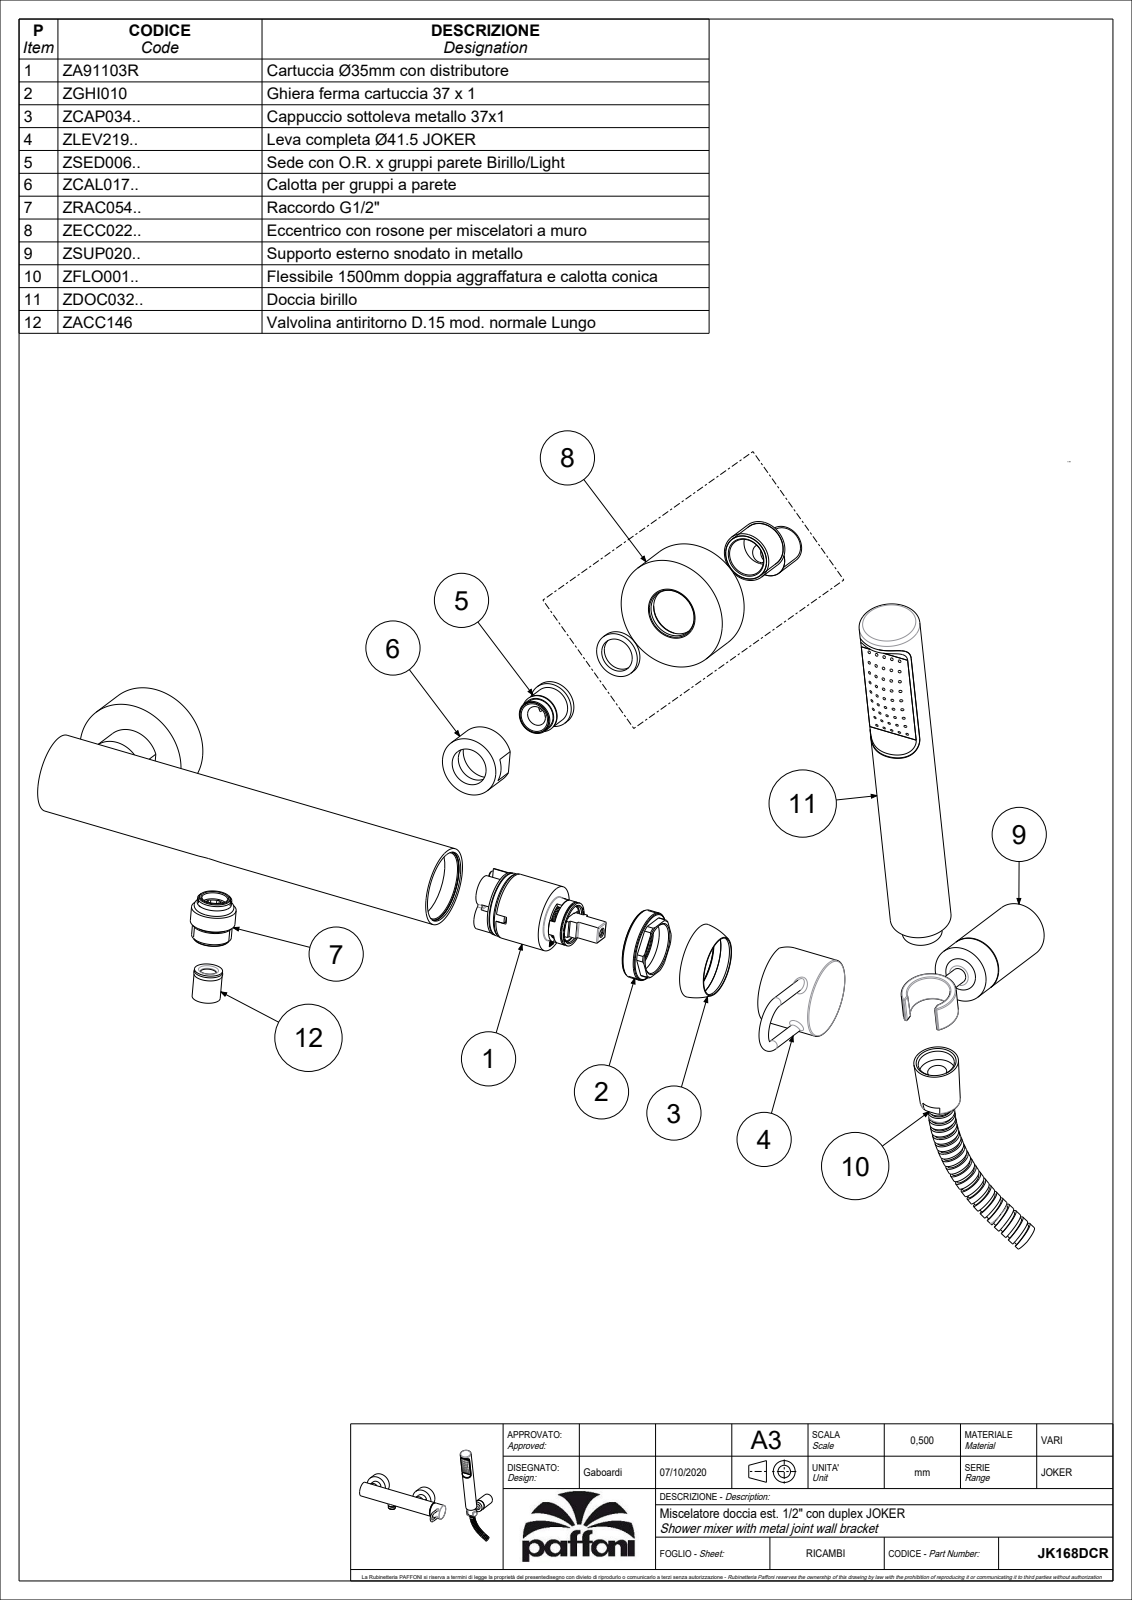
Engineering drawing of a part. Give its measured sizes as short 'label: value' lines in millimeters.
name: JK168DCR
written by: CREO PARAMETRIC BY PTC INC, 2020044 (CONFIG_CONTROL_DESIGN)
unit: mm
bodies: 3 solids, 1496 faces (724 planar, 479 cylindrical, 293 other)
size: 427.94 × 316.37 × 192.55
volume: 468 769 mm³; area: 185 223 mm²
holes: 45× ⌀1.5, 6× ⌀7.5, 3× ⌀8, 3× ⌀9, 3× ⌀12, 3× ⌀16.7, 2× ⌀4, 2× ⌀10.5, 2× ⌀18, 2× ⌀20, 2× ⌀24.5, 2× ⌀25.5
bosses: 3× ⌀5, 2× ⌀59.7, 2× ⌀41.5, 2× ⌀31.5, 2× ⌀24, 2× ⌀23.5, 2× ⌀19.7, 1× ⌀35
rounds: 54× R0.5, 11× R0.15, 9× R0.3, 4× R1, 4× R7, 2× R1.56, 2× R4.5, 2× R7.8
face distances: 5, 25, 10, 20, 23, 18, 43, 3, 13, 23.5
hole spacings: 7.91, 20.01, 6.5, 13, 26.38, 13.76, 4.5, 11.1
